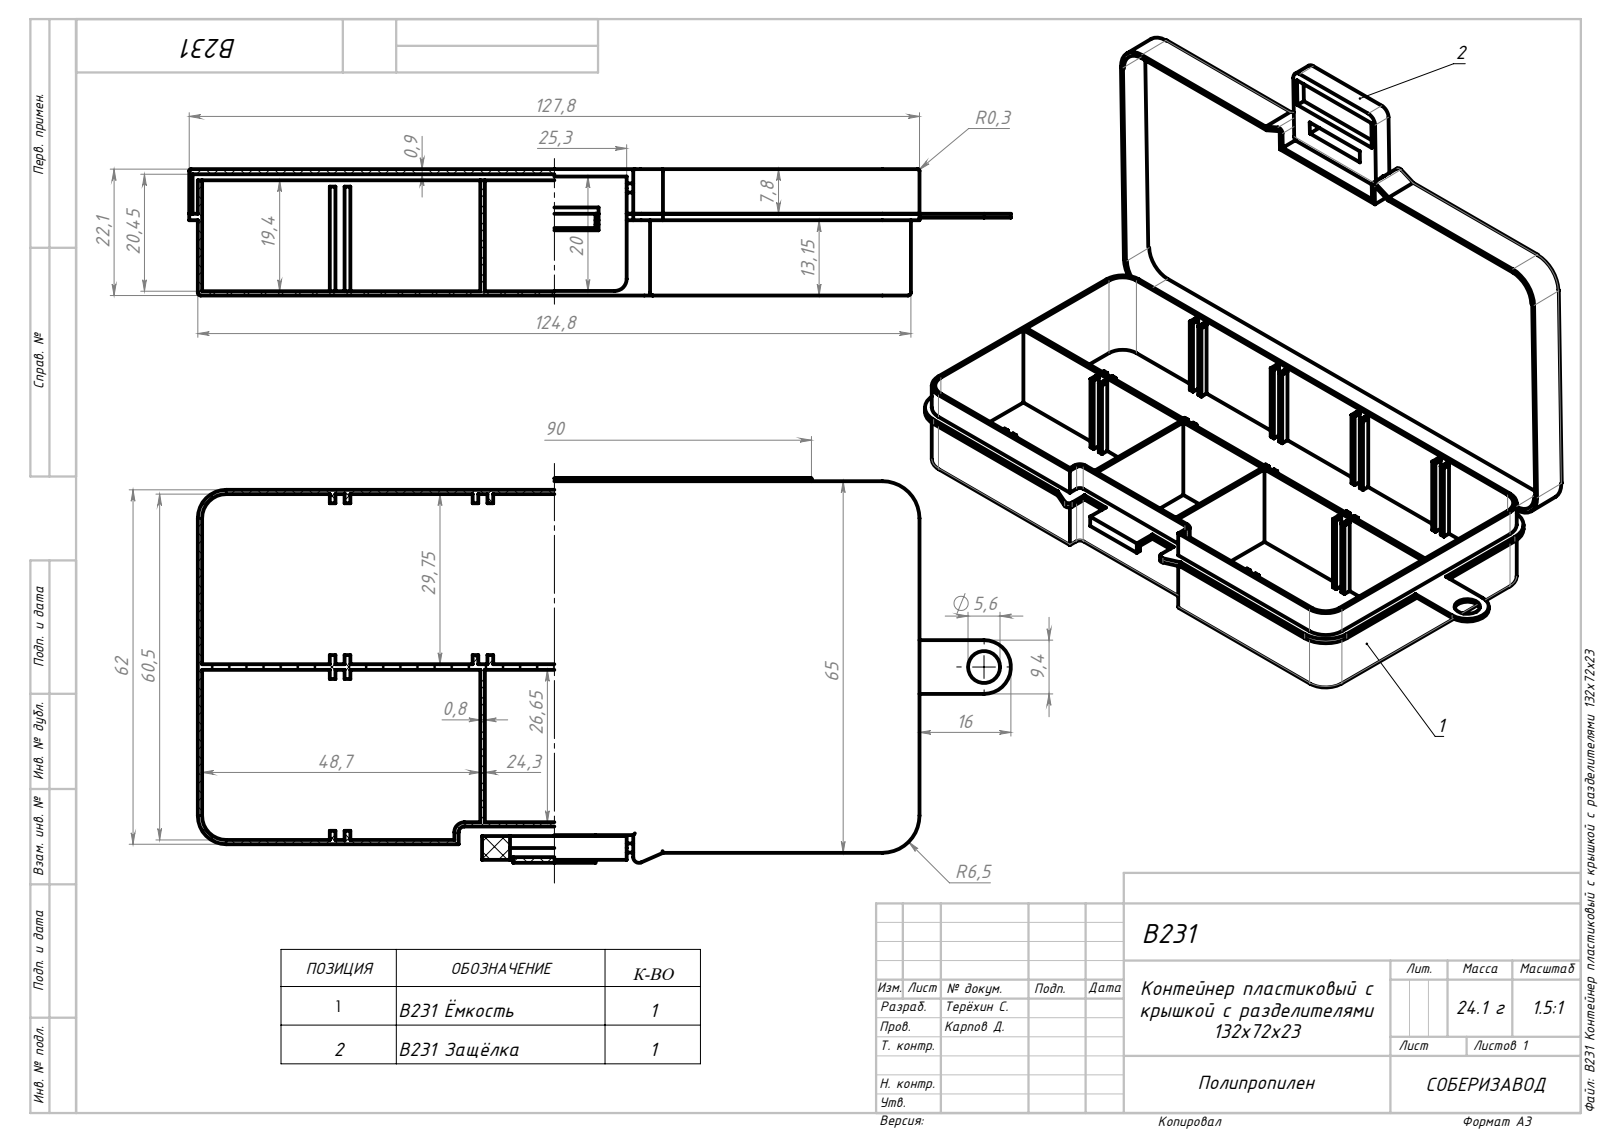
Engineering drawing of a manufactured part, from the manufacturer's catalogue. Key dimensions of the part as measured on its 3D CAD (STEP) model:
Part name (STEP PRODUCT): B231 Ёмкость; B231 Крышка; B231 Защёлка; B231 Контейнер пластиковый с крышкой с разделителями 132x72x23
STEP written by: SolidWorks 2021 (AUTOMOTIVE_DESIGN)
Units: millimetres
Bodies: 3 solids, 290 faces (204 planar, 68 cylindrical, 18 other)
Overall size (bounding box): 143.8 × 67.25 × 22.1
Volume: 26 915 mm³ · Surface area: 63 232 mm²
Round holes (diameter × count): ⌀1.99 ×1, ⌀5.6 ×1
Round bosses / shafts (diameter × count): ⌀1.6 ×1
Partial cylindrical surfaces — rounded edges, fillets, slot ends (radius × count): R0.3 ×9, R0.5 ×7, R1 ×4, R4.25 ×4, R5 ×4, R5.6 ×4, R6.5 ×4, R2.08 ×3
Main face-to-face distances: 0.75, 0.9, 21.2, 22.1, 20.45, 21.35, 31.5, 30.75, 30.5, 29.75
